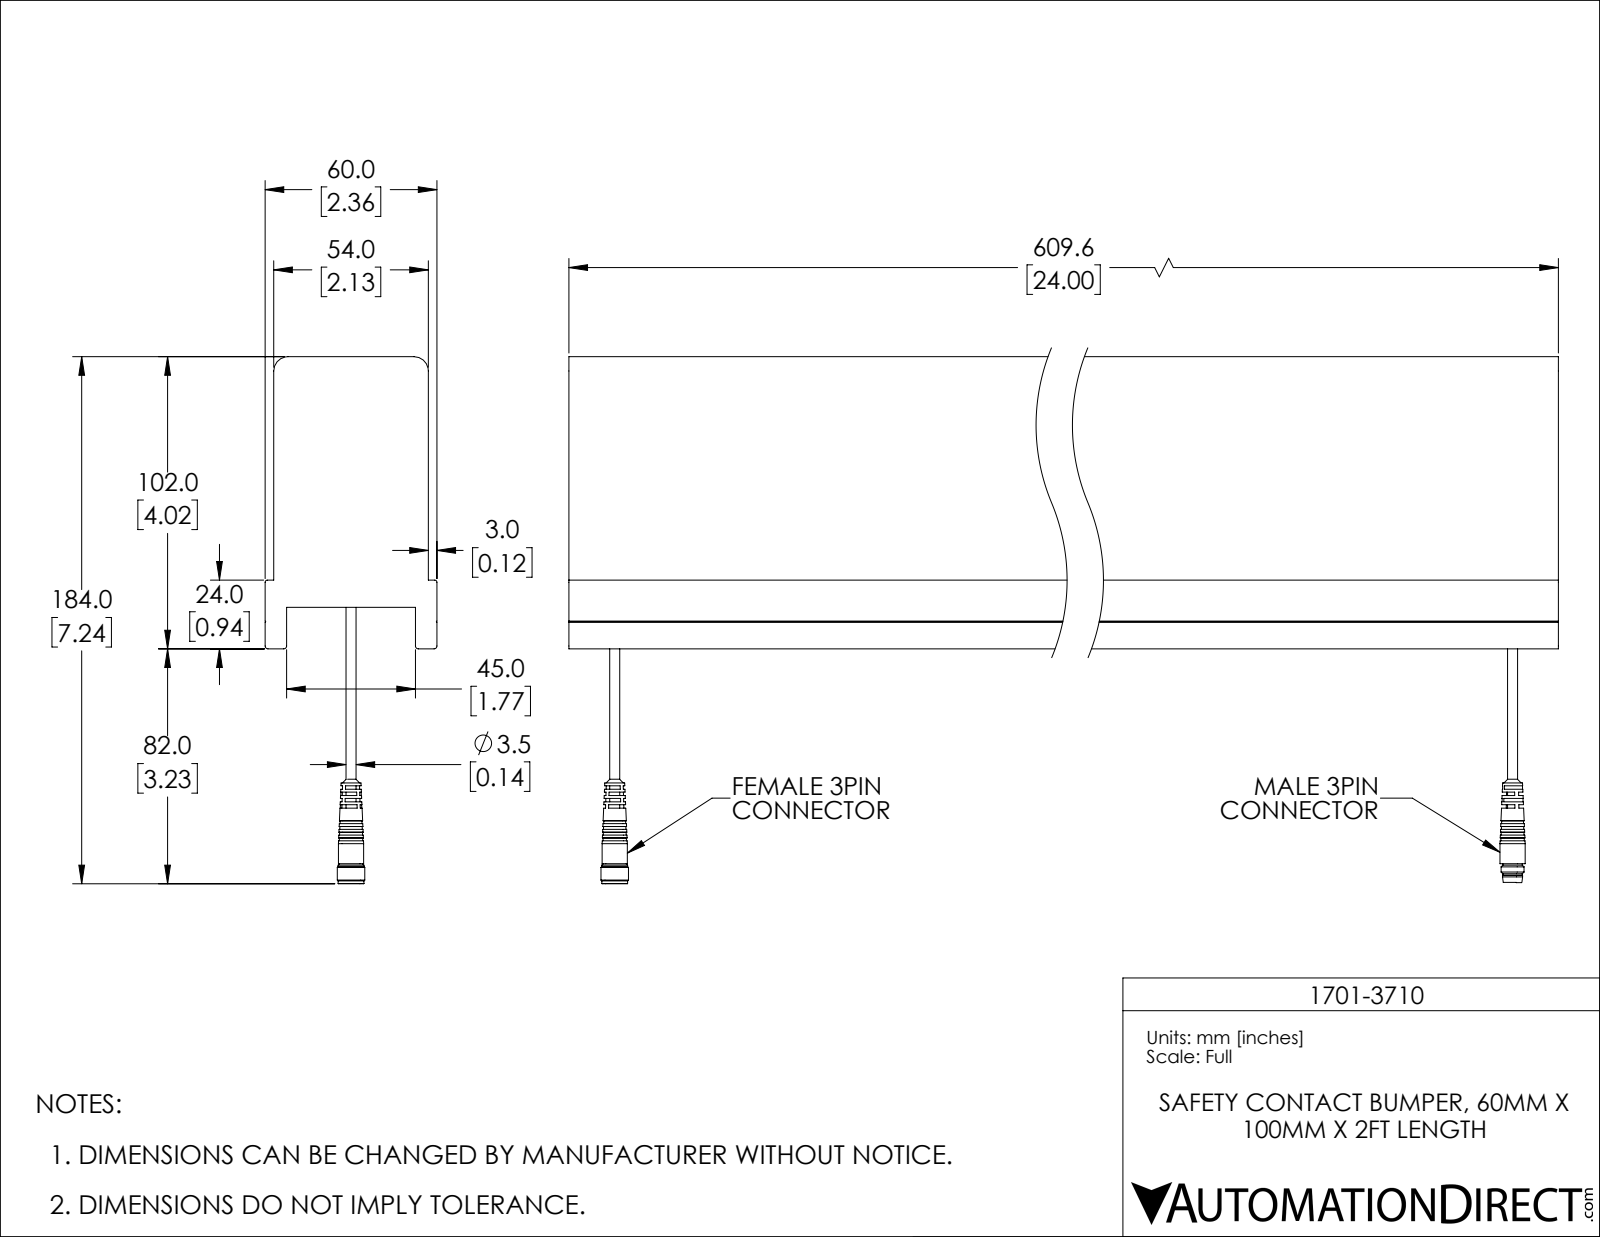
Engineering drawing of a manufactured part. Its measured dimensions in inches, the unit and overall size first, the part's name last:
Units: inches
Overall size (bounding box): 24 × 7.244 × 2.362
Round holes (diameter × count): ⌀0.063 ×3, ⌀0.134 ×2, ⌀0.228 ×1, ⌀0.232 ×1, ⌀0.272 ×1, ⌀0.283 ×1
Round bosses / shafts (diameter × count): ⌀0.047 ×16, ⌀0.031 ×4, ⌀0.039 ×3, ⌀0.346 ×2, ⌀0.138 ×2, ⌀0.378 ×1, ⌀0.354 ×1, ⌀0.315 ×1
Main face-to-face distances: 2.126, 3.445, 0.118, 2.244, 0.295, 2.067, 0.177, 1.949, 2.362, 1.772
Hole centre spacings: 0.069, 0.098, 22.789, 0.138, 22.691, 22.74
Volume: 185.8 in³ · Surface area: 351.5 in²
Bodies: 20 solids, 294 faces (138 planar, 59 cylindrical, 97 other)
Part name (STEP PRODUCT): 1701-3710
STEP written by: SolidWorks 2018 (AUTOMOTIVE_DESIGN)
